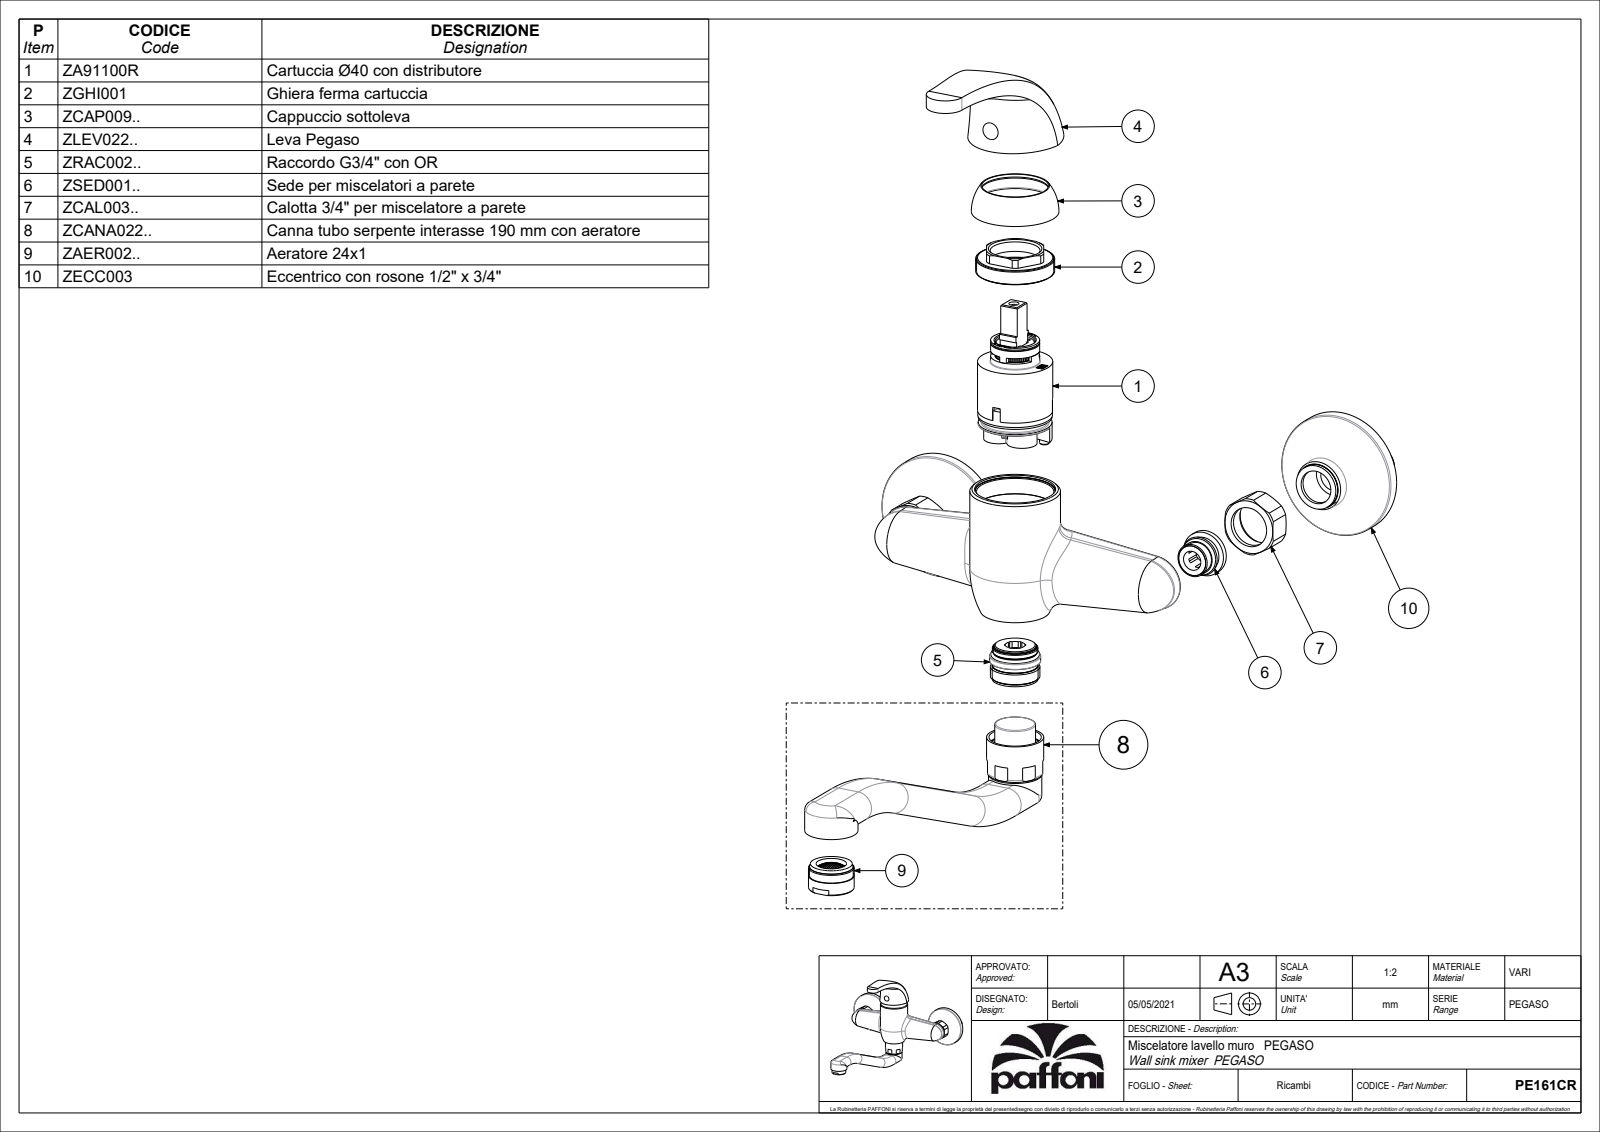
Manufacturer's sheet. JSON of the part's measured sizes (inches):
{"part_name": "PE161CR_SW0001", "step_written_by": "CREO PARAMETRIC BY PTC INC, 2022124 (CONFIG_CONTROL_DESIGN)", "units": "inches", "bodies": {"solids": 4, "faces": 1258, "planar": 974, "cylindrical": 114, "other": 170}, "overall_size": [11.063, 8.504, 6.314], "volume_in3": 24.84, "surface_area_in2": 163.4, "round_holes": [[0.63, 2], [1.051, 2], [0.236, 1], [0.669, 1], [0.677, 1], [0.728, 1], [0.787, 1], [0.827, 1], [0.917, 1], [0.953, 1], [1.063, 1], [1.083, 1]], "round_bosses_or_shafts": [[2.598, 2], [1.102, 2], [1.039, 2], [0.827, 2], [1.874, 1], [1.181, 1], [0.945, 1], [0.768, 1]], "partial_cylinders_radius": [[0.039, 8], [0.283, 6], [0.315, 6], [0.512, 2], [0.61, 2], [3.701, 2], [3.732, 2], [4.299, 2]], "face_to_face_distances": [0.031, 0.598, 1.142, 0.059, 0.63, 0.567, 1.299, 1.358, 0.638, 3.248], "hole_center_spacings": [3.831, 5.906, 7.598]}
